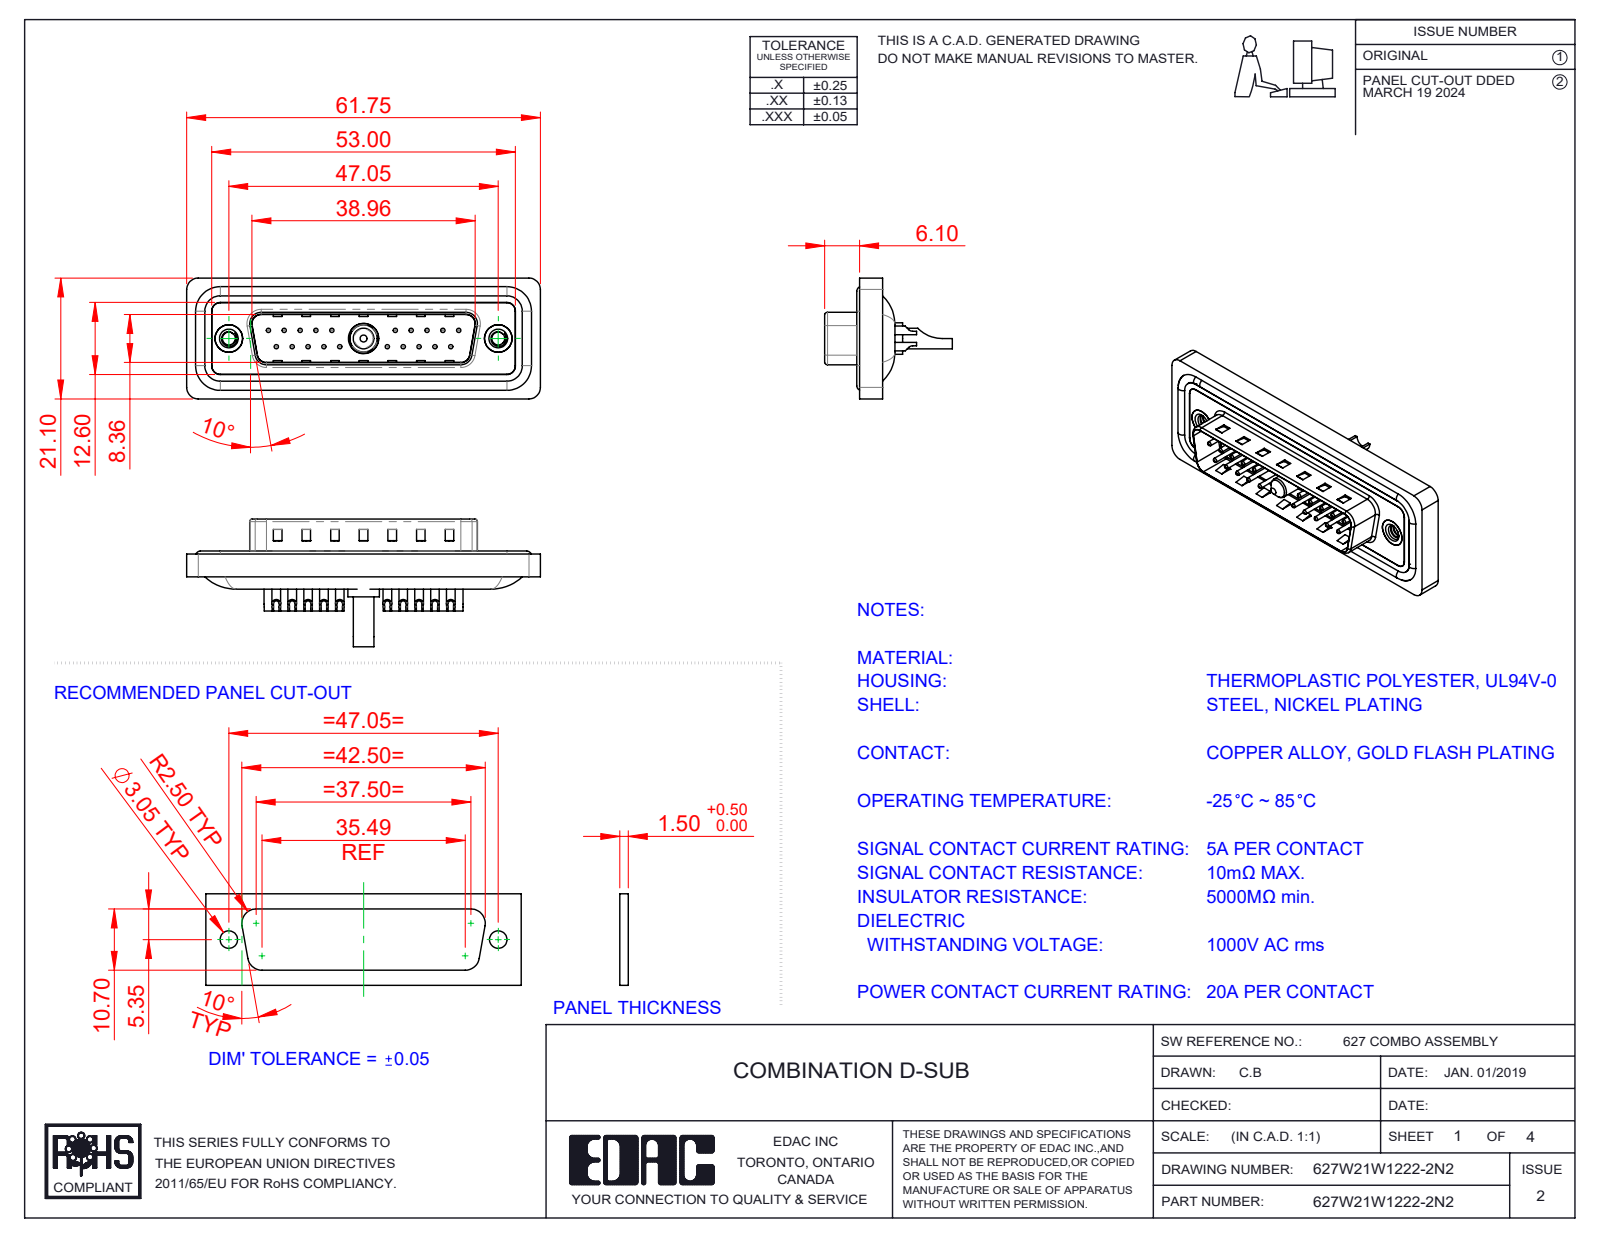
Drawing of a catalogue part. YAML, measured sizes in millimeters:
part_name: "627Combo Contact Row 1_22; 627Combo Shell Rear_25 Contacts; 627Combo Waterproof Housing_25 Contacts; 627W21W1222-2N2 (+5 more)"
step_written_by: "SolidWorks 2023 (CONFIG_CONTROL_DESIGN)"
units: millimeters
bodies: {solids: 29, faces: 1269, planar: 402, cylindrical: 530, other: 337}
overall_size: [61.75, 22.3, 21.1]
volume: 7241
surface_area: 12195
round_holes:
  - {diameter: 0.75, count: 20}
  - {diameter: 1, count: 20}
  - {diameter: 1.6, count: 20}
  - {diameter: 2, count: 20}
  - {diameter: 2.26, count: 2}
  - {diameter: 4, count: 2}
  - {diameter: 4.8, count: 2}
  - {diameter: 5, count: 2}
  - {diameter: 2.7, count: 1}
  - {diameter: 4.85, count: 1}
  - {diameter: 5.3, count: 1}
round_bosses_or_shafts:
  - {diameter: 1.5, count: 20}
  - {diameter: 1.6, count: 4}
  - {diameter: 4.9, count: 2}
  - {diameter: 5.5, count: 1}
  - {diameter: 5.2, count: 1}
  - {diameter: 4.75, count: 1}
  - {diameter: 3.75, count: 1}
  - {diameter: 3.6, count: 1}
partial_cylinders:
  - {radius: 1.5, count: 22}
  - {radius: 2, count: 18}
  - {radius: 0.5, count: 8}
  - {radius: 1.6, count: 8}
  - {radius: 1, count: 6}
  - {radius: 0.25, count: 4}
  - {radius: 0.6, count: 4}
  - {radius: 0.65, count: 4}
face_to_face_distances: [0.4, 1.5, 1.1, 1.6, 0.5, 3.1, 2.9, 4.1, 0.82, 9.58]
hole_center_spacings: [3.16, 2.77, 5.54, 8.31, 5.04, 19.39, 20.97, 22.16]
